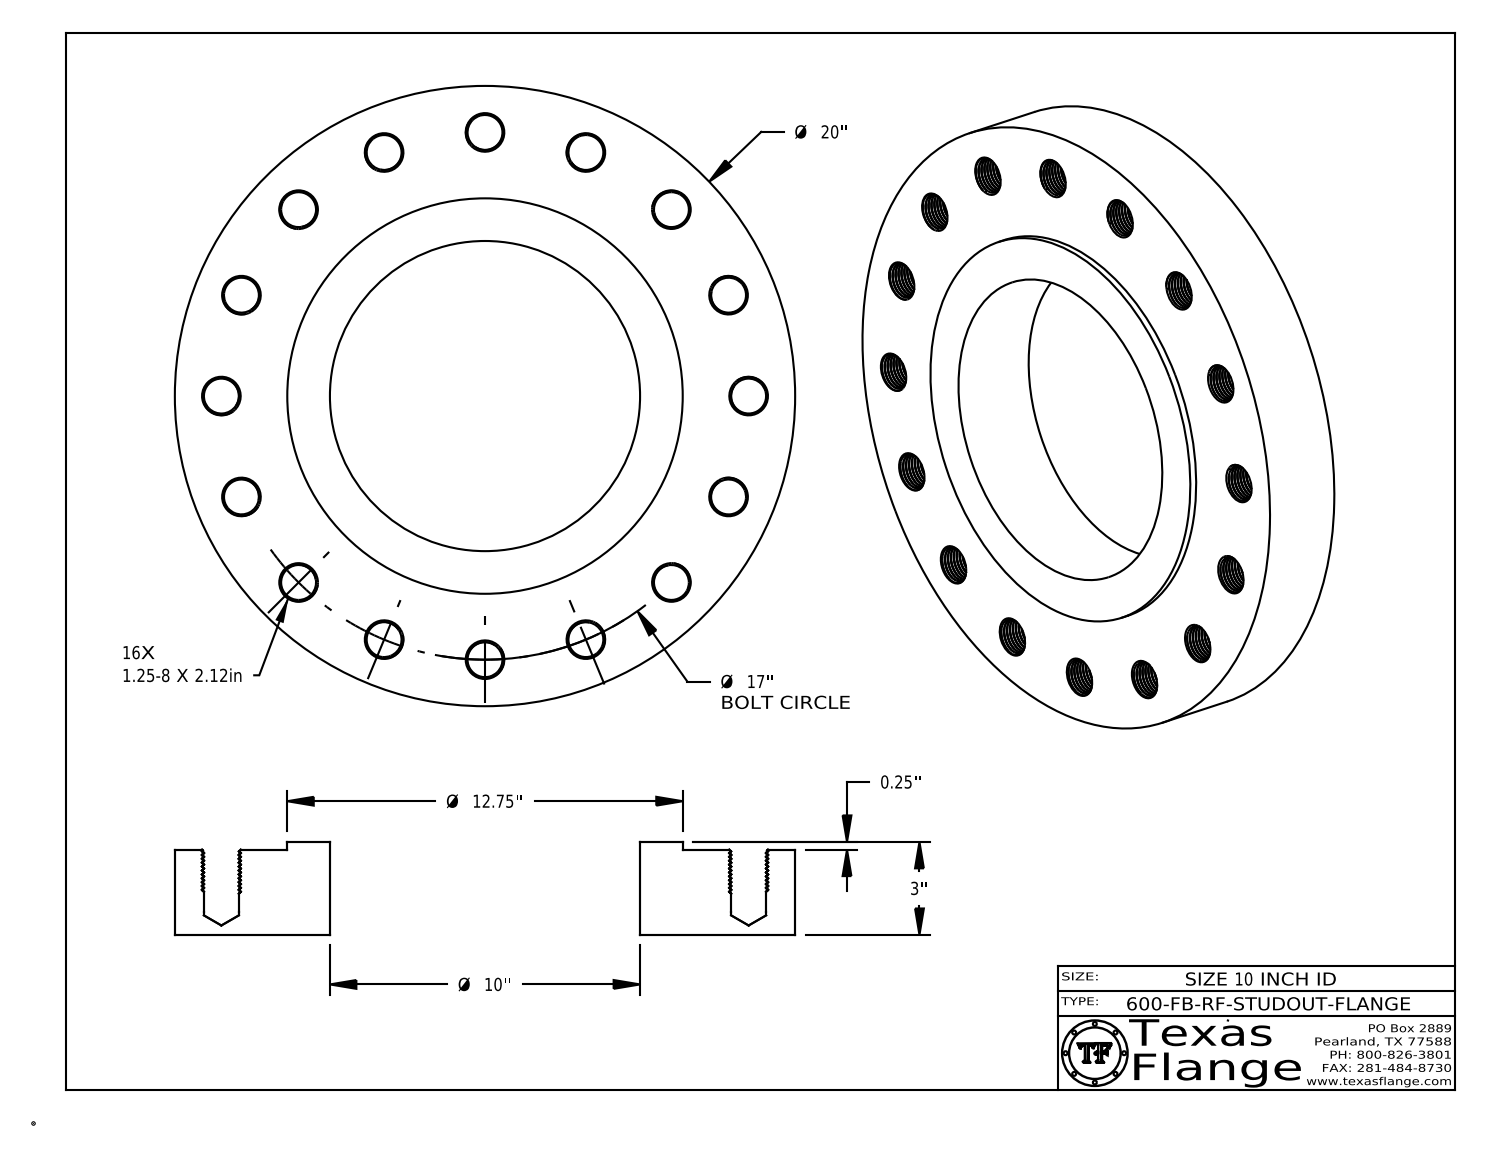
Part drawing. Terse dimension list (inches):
name: 10-600-FB-RF-STUDOUT-FLANGE
written by: CATIA V5 STEP AP214 (AUTOMOTIVE_DESIGN)
unit: in
bodies: 1 solid, 1642 faces (368 planar, 410 cylindrical, 864 other)
size: 20 × 20 × 3
volume: 622.3 in³; area: 906.3 in²
holes: 16× ⌀1.125, 1× ⌀1, 1× ⌀10
bosses: 8× ⌀0.061, 1× ⌀20, 1× ⌀12.75, 1× ⌀0.788
face distances: 2.75, 0.25, 3, 2.985, 2.735, 0.015, 0.298, 0.293, 0.054, 0.248
hole spacings: 3.317, 14.135, 6.506, 8.5, 12.021, 9.444, 9.445, 15.706
